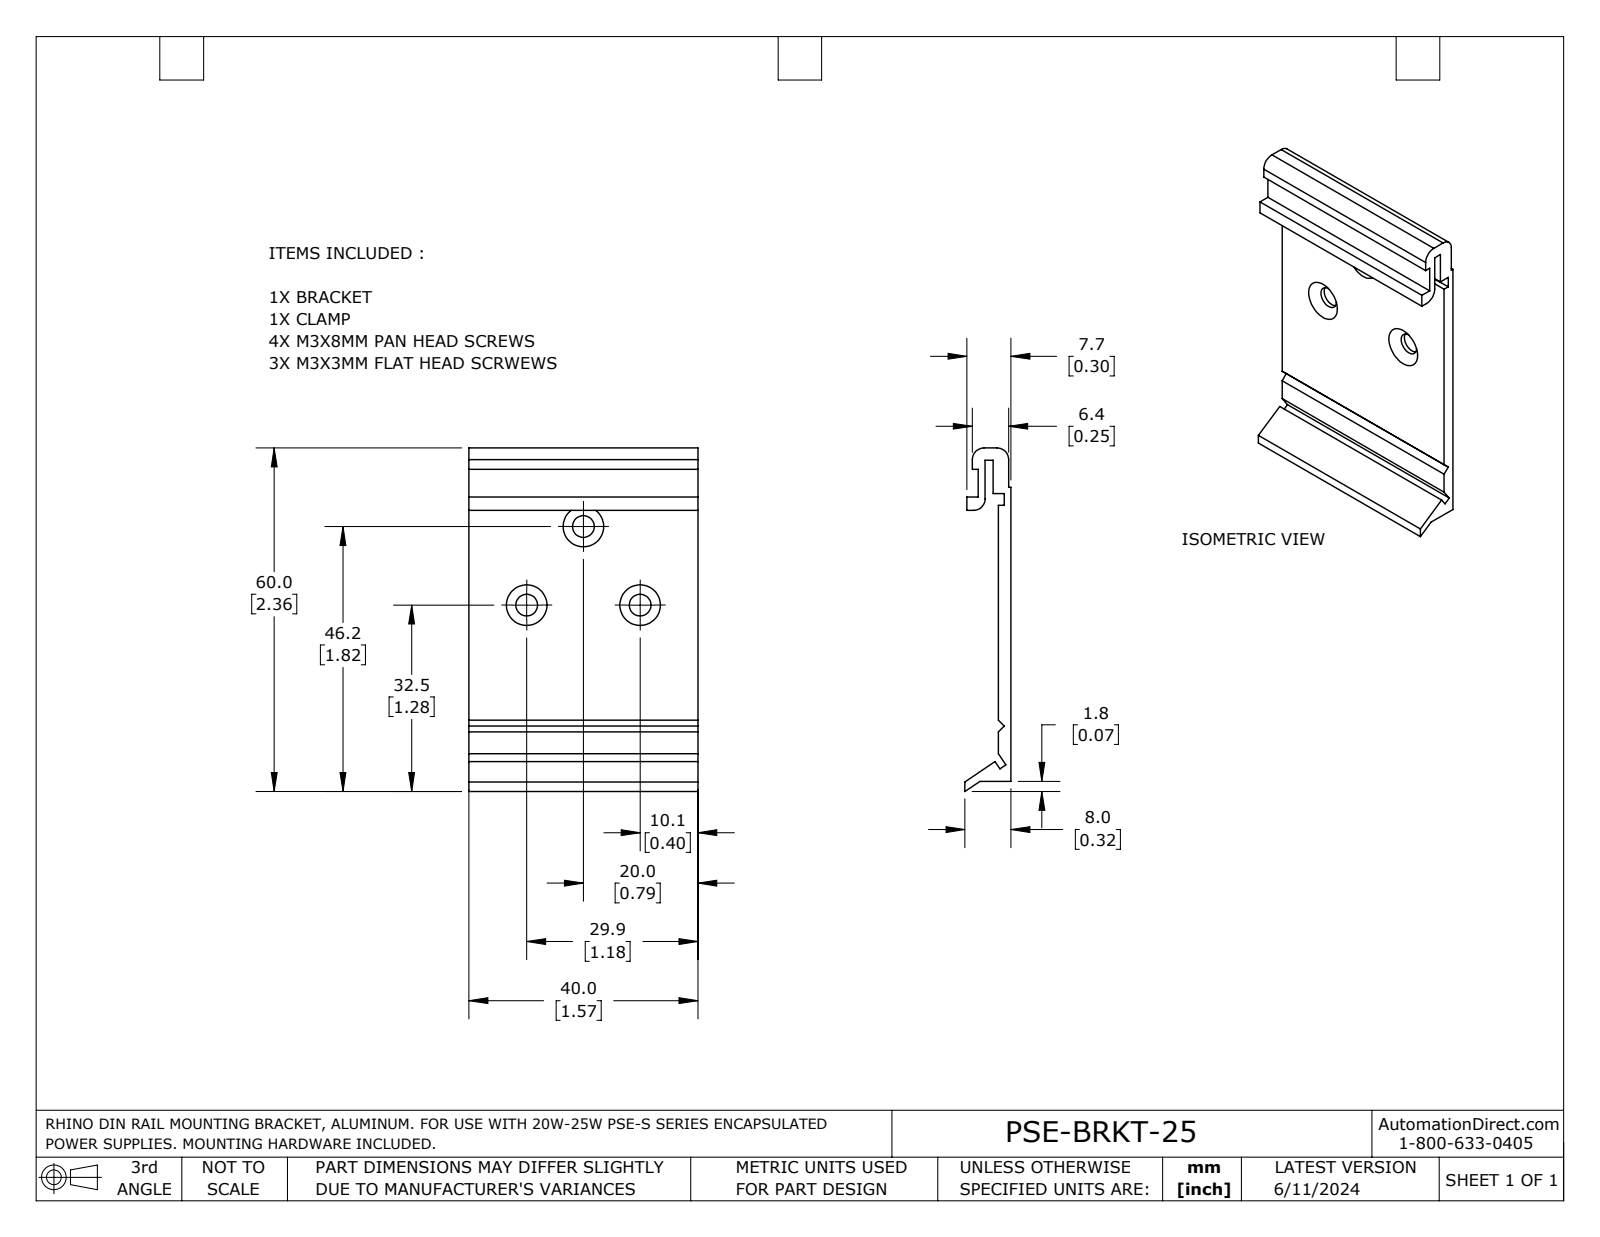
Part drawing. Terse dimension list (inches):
name: PSE-BRKT-25
written by: SolidWorks 2023 (AUTOMOTIVE_DESIGN)
unit: in
bodies: 1 solid, 38 faces (29 planar, 6 cylindrical, 3 other)
size: 2.361 × 1.574 × 0.317
volume: 0.387 in³; area: 10.78 in²
holes: 3× ⌀0.15
rounds: 3× R0.08
face distances: 0.086, 0.091, 0.177, 0.139, 0.055, 0.037, 0.122, 0.162, 0.107, 0.07
hole spacings: 0.666, 0.78
